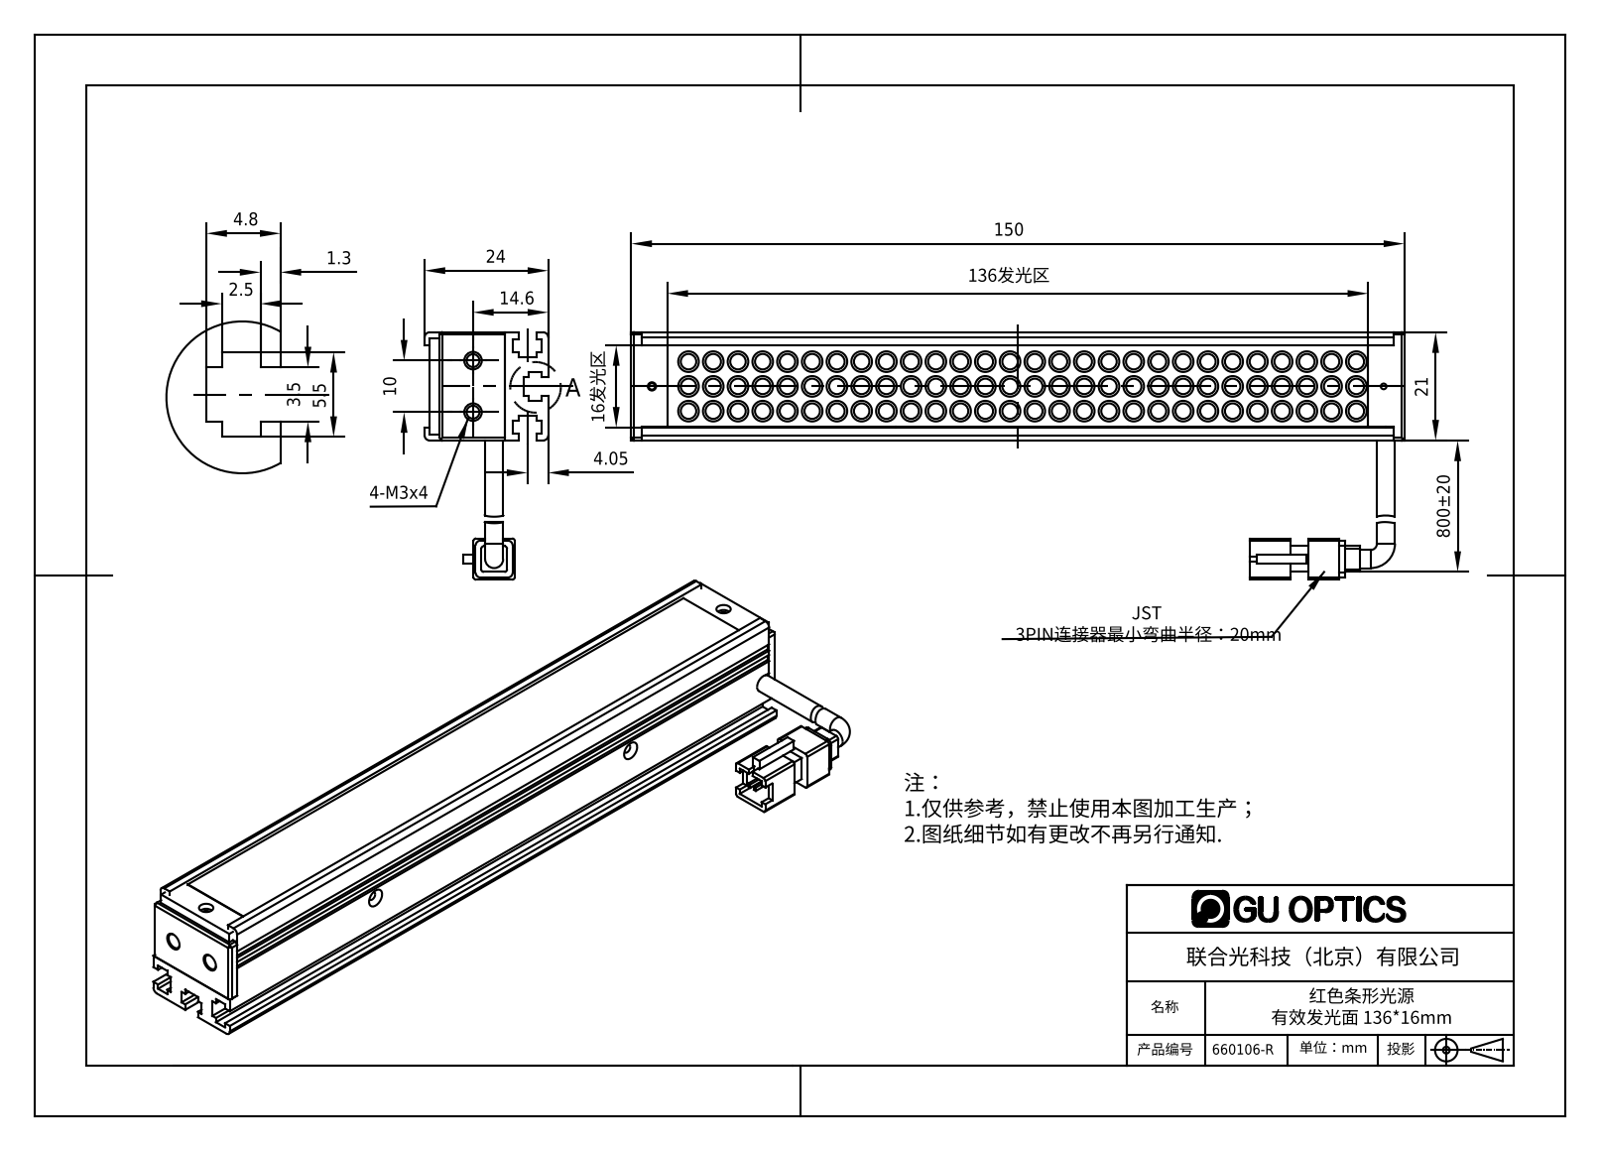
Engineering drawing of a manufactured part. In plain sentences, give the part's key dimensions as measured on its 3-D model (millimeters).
The part is named "660106-R". Its 3-D file was written by "SolidWorks 2016 (AUTOMOTIVE_DESIGN)". It is 8 solids with 941 faces: 335 planar, 419 cylindrical and 187 other. Overall it measures 150 by 48 by 24 millimeters. Its volume is 43 647 cubic millimeters and its surface area 48 667 square millimeters. Round holes: 5 of diameter 1.6, 2 of diameter 1.5, 2 of diameter 1.7, 2 of diameter 2.5, 2 of diameter 2.8, 2 of diameter 3, 1 of diameter 1.1, 1 of diameter 1.25, 1 of diameter 2. Round bosses or shafts: 84 of diameter 4, 84 of diameter 3, 2 of diameter 3.5. Partial cylindrical surfaces (rounded edges, fillets, slot ends): 12 of radius 1, 8 of radius 0.5, 1 of radius 1.65. The main face-to-face distances are 1, 2.5, 2, 14.7, 18.5, 4, 2.1, 14.6, 1.3, 3.5. The hole center spacings are 142, 7, 36.04, 36.4, 106.01, 106.14, 142.17, 10.
